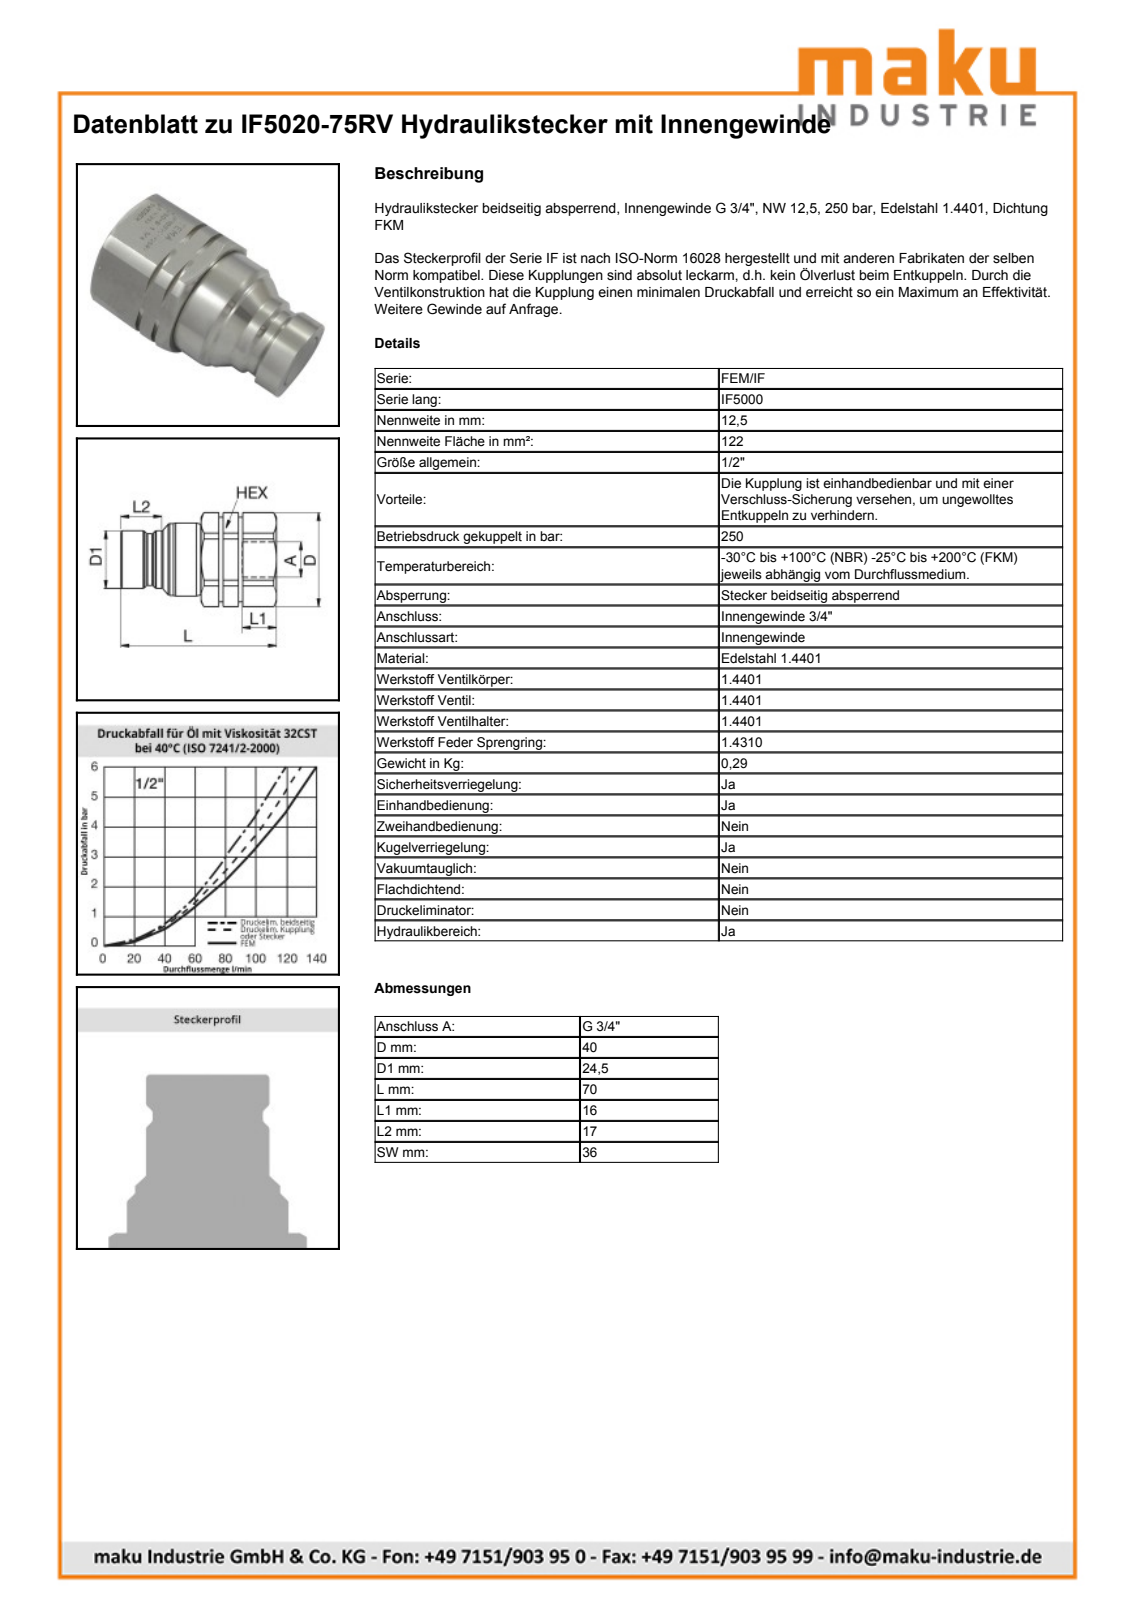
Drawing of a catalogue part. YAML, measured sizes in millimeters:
part_name: "IF5020-75RV"
step_written_by: "SolidWorks 2009 (AUTOMOTIVE_DESIGN)"
units: millimeters
bodies: {solids: 1, faces: 133, planar: 49, cylindrical: 38, other: 46}
overall_size: [70.1, 40, 36]
volume: 49814
surface_area: 11253
round_holes:
  - {diameter: 18, count: 1}
  - {diameter: 24.12, count: 1}
round_bosses_or_shafts:
  - {diameter: 36, count: 1}
  - {diameter: 31, count: 1}
  - {diameter: 30.5, count: 1}
  - {diameter: 30, count: 1}
  - {diameter: 24.5, count: 1}
  - {diameter: 22, count: 1}
partial_cylinders:
  - {radius: 20, count: 1}
face_to_face_distances: [36, 22.1, 13.9, 70.1, 48, 34.1, 70.04, 47.94, 34.04, 20.15]
